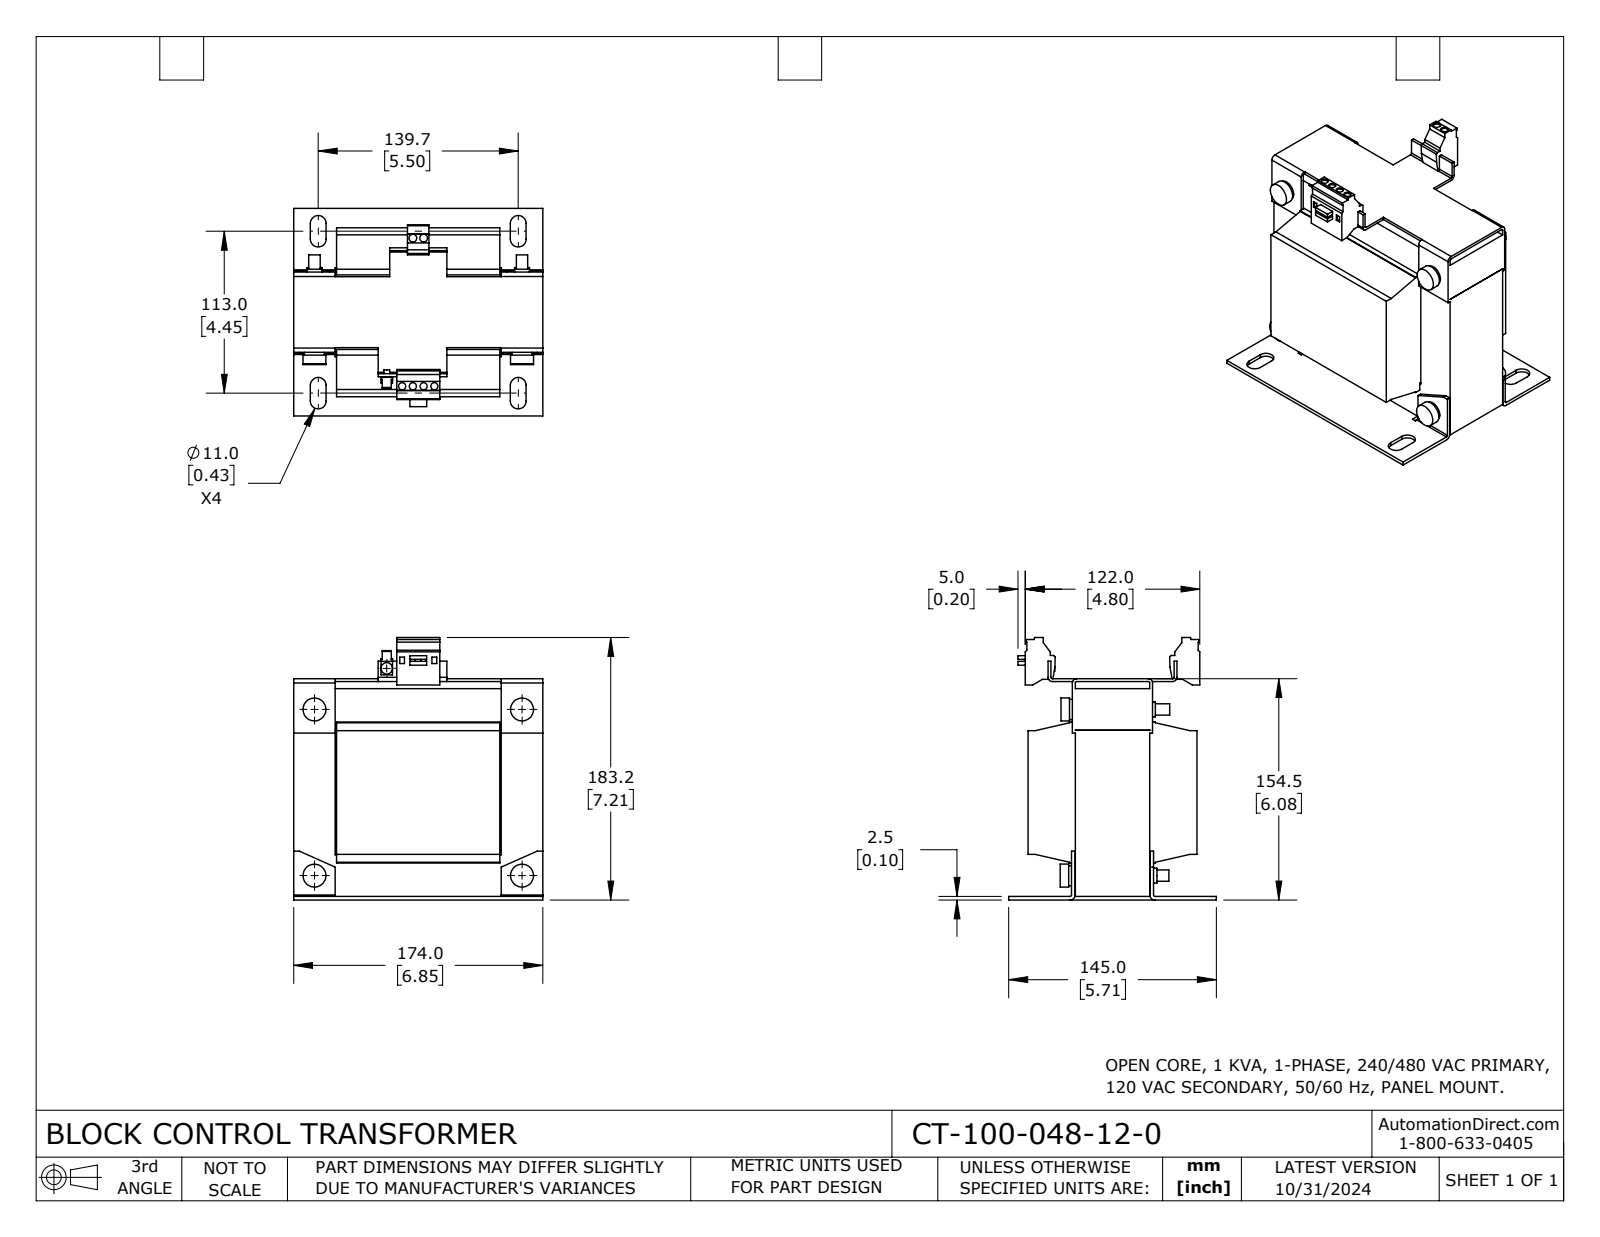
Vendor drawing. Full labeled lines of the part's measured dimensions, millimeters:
Part name (STEP PRODUCT): CT-100-048-12-0
STEP written by: SolidWorks 2023 (CONFIG_CONTROL_DESIGN)
Units: millimetres
Bodies: 1 solid, 339 faces (247 planar, 92 cylindrical, 0 other)
Overall size (bounding box): 183.2 × 174 × 145
Volume: 2 116 000 mm³ · Surface area: 224 800 mm²
Round holes (diameter × count): ⌀5 ×4, ⌀5.4 ×2
Round bosses / shafts (diameter × count): ⌀8 ×5, ⌀16 ×4, ⌀14 ×4, ⌀10.5 ×4, ⌀10 ×2, ⌀4 ×1
Partial cylindrical surfaces — rounded edges, fillets, slot ends (radius × count): R5.5 ×8, R1 ×6, R3 ×4, R3.5 ×2
Main face-to-face distances: 116, 29, 2.5, 33, 85, 145, 30, 144, 2, 118.5
Hole centre spacings: 7.5, 103.7, 15, 103.4, 104.5, 22.5
